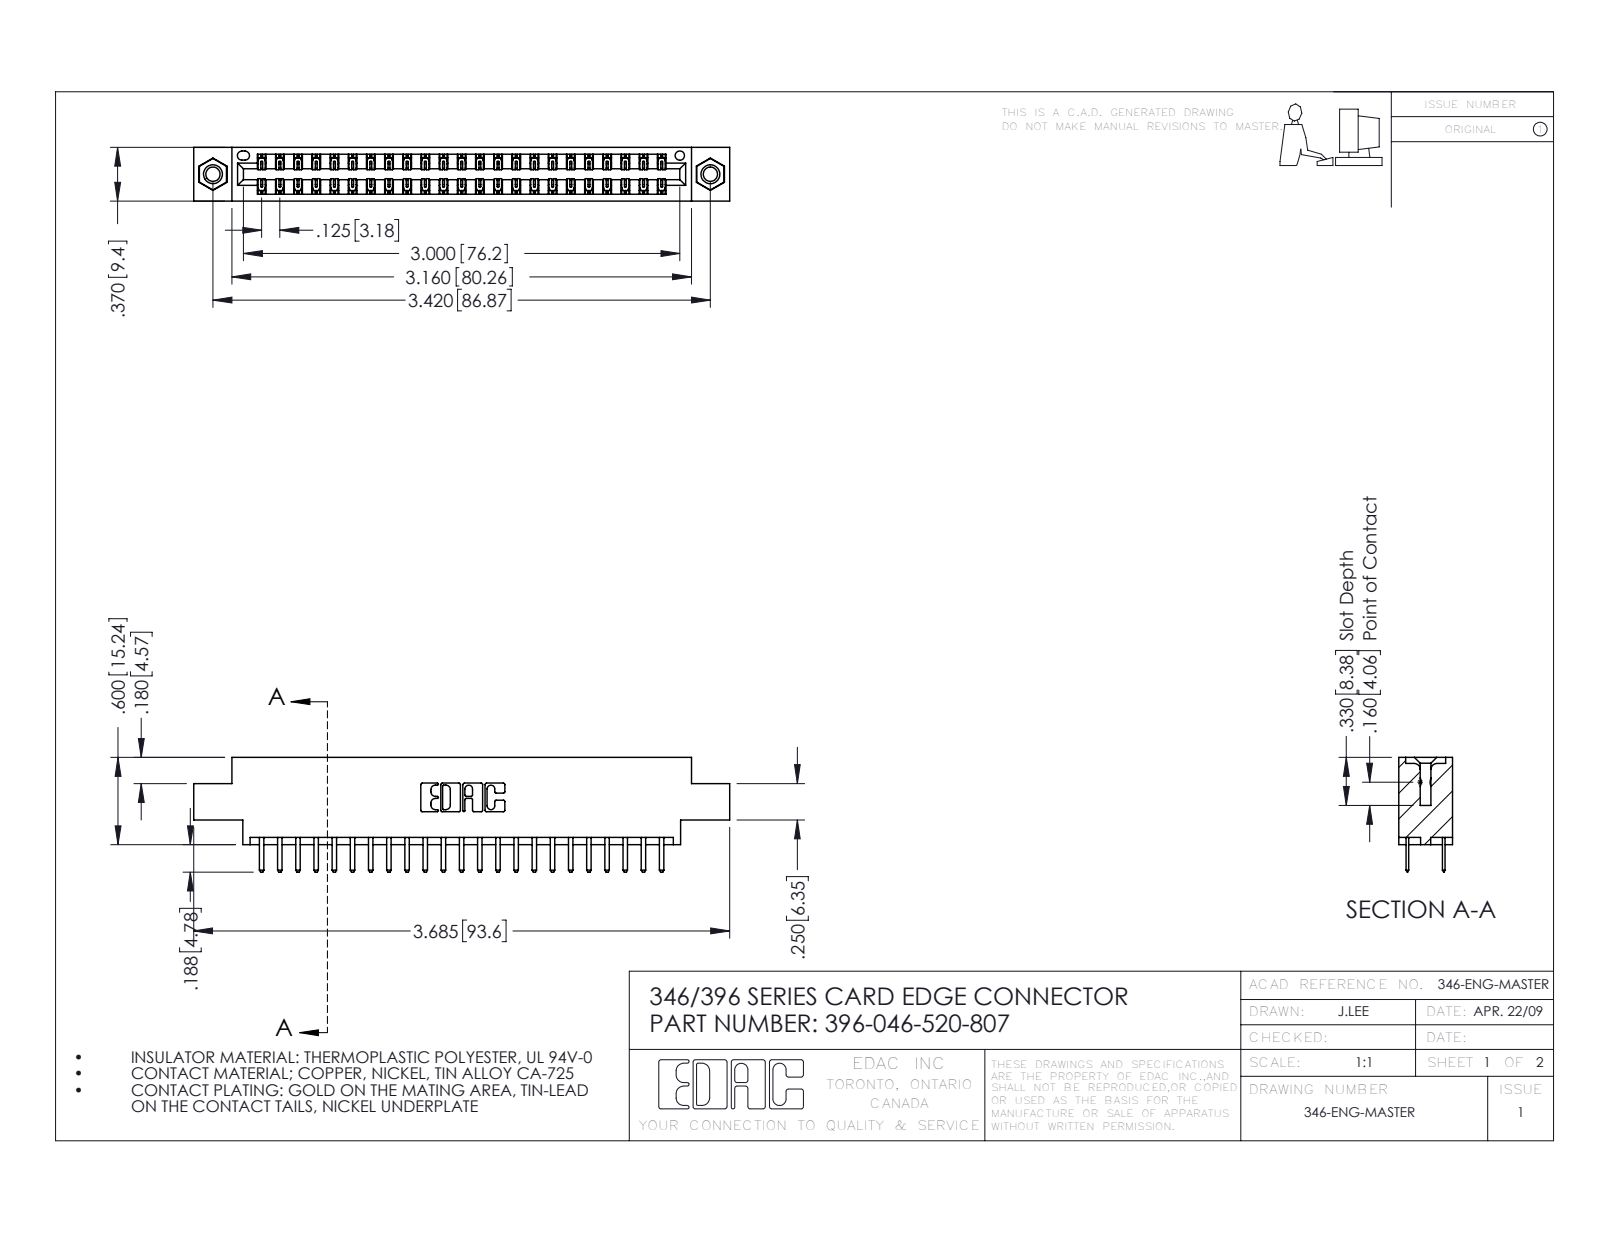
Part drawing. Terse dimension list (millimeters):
name: 346 Part_0.170 Offset - 0.156 Dia-TI; 345-292-001_345-293-120; 345-250-001_345-250-005-103; 396-046-520-807
written by: SolidWorks 2016 (CONFIG_CONTROL_DESIGN)
unit: mm
bodies: 49 solids, 2762 faces (1814 planar, 932 cylindrical, 16 other)
size: 93.6 × 20 × 9.4
volume: 8 780 mm³; area: 11 950 mm²
holes: 2× ⌀2.5, 2× ⌀3.2, 2× ⌀4, 1× ⌀1.6
bosses: 2× ⌀3.9
rounds: 69× R0.2, 50× R0.3, 22× R0.3, 6× R0.2, 6× R0.8, 3× R0.7, 2× R0.4, 2× R0.6
face distances: 1.2, 8.2, 6.4, 9.4, 7, 1.8, 7.6, 0.6, 5.6, 3.8
hole spacings: 6.2, 81.6, 86.9
